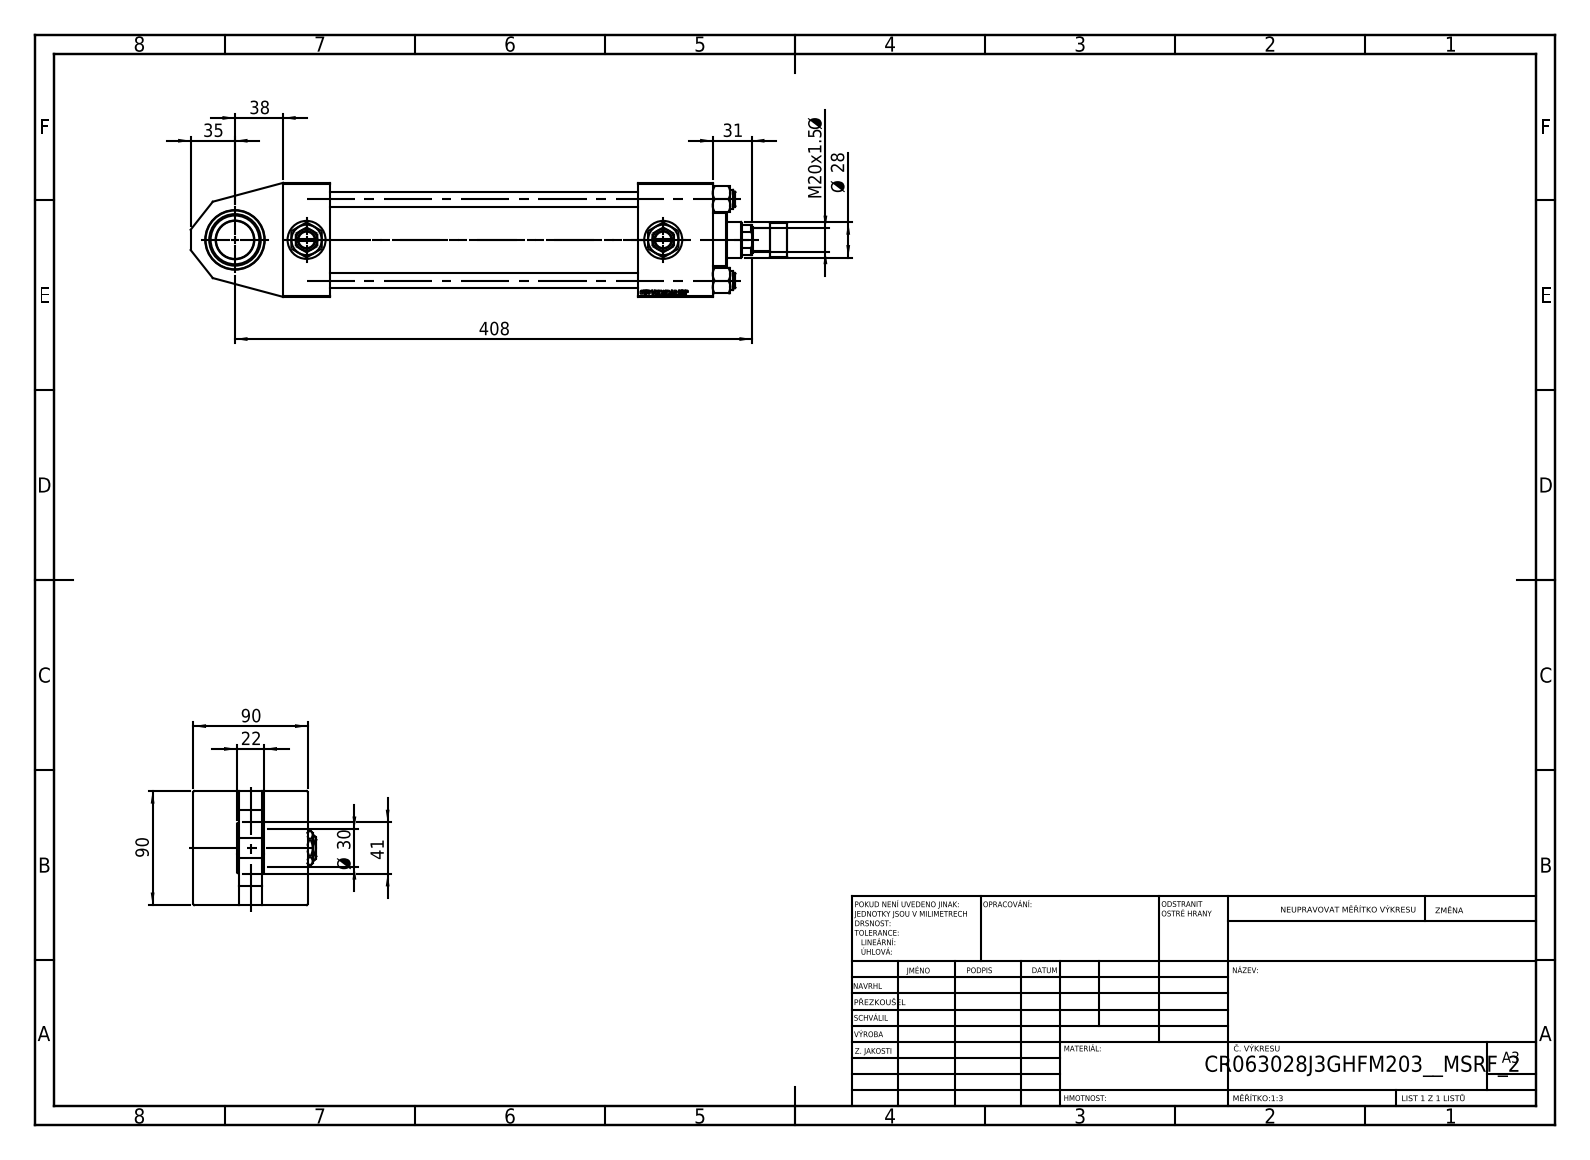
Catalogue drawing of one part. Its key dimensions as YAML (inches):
part_name: "V215CR_J_Body; V215CR_ROD_END_F; V215CR_VCP_J; V215_VC_A (+4 more)"
step_written_by: "SolidWorks 2019 (CONFIG_CONTROL_DESIGN)"
units: inches
bodies: {solids: 15, faces: 1260, planar: 568, cylindrical: 104, other: 588}
overall_size: [18.543, 3.819, 3.543]
volume: 82.2
surface_area: 508.8
round_holes:
  - {diameter: 0.472, count: 4}
  - {diameter: 1.181, count: 3}
  - {diameter: 0.098, count: 2}
  - {diameter: 0.276, count: 2}
  - {diameter: 0.825, count: 2}
  - {diameter: 0.728, count: 1}
  - {diameter: 1.102, count: 1}
  - {diameter: 1.22, count: 1}
  - {diameter: 1.85, count: 1}
  - {diameter: 1.969, count: 1}
  - {diameter: 2.362, count: 1}
  - {diameter: 2.48, count: 1}
round_bosses_or_shafts:
  - {diameter: 0.591, count: 4}
  - {diameter: 2.717, count: 1}
  - {diameter: 1.654, count: 1}
  - {diameter: 1.063, count: 1}
  - {diameter: 0.709, count: 1}
face_to_face_distances: [3.543, 2.126, 1.417, 11.89, 1.457, 13.346, 2.323, 11.024, 9.567, 0.709]
hole_center_spacings: [1.275, 1.79, 2.531, 2.694, 1.112, 2.224, 3.58, 11.083]
